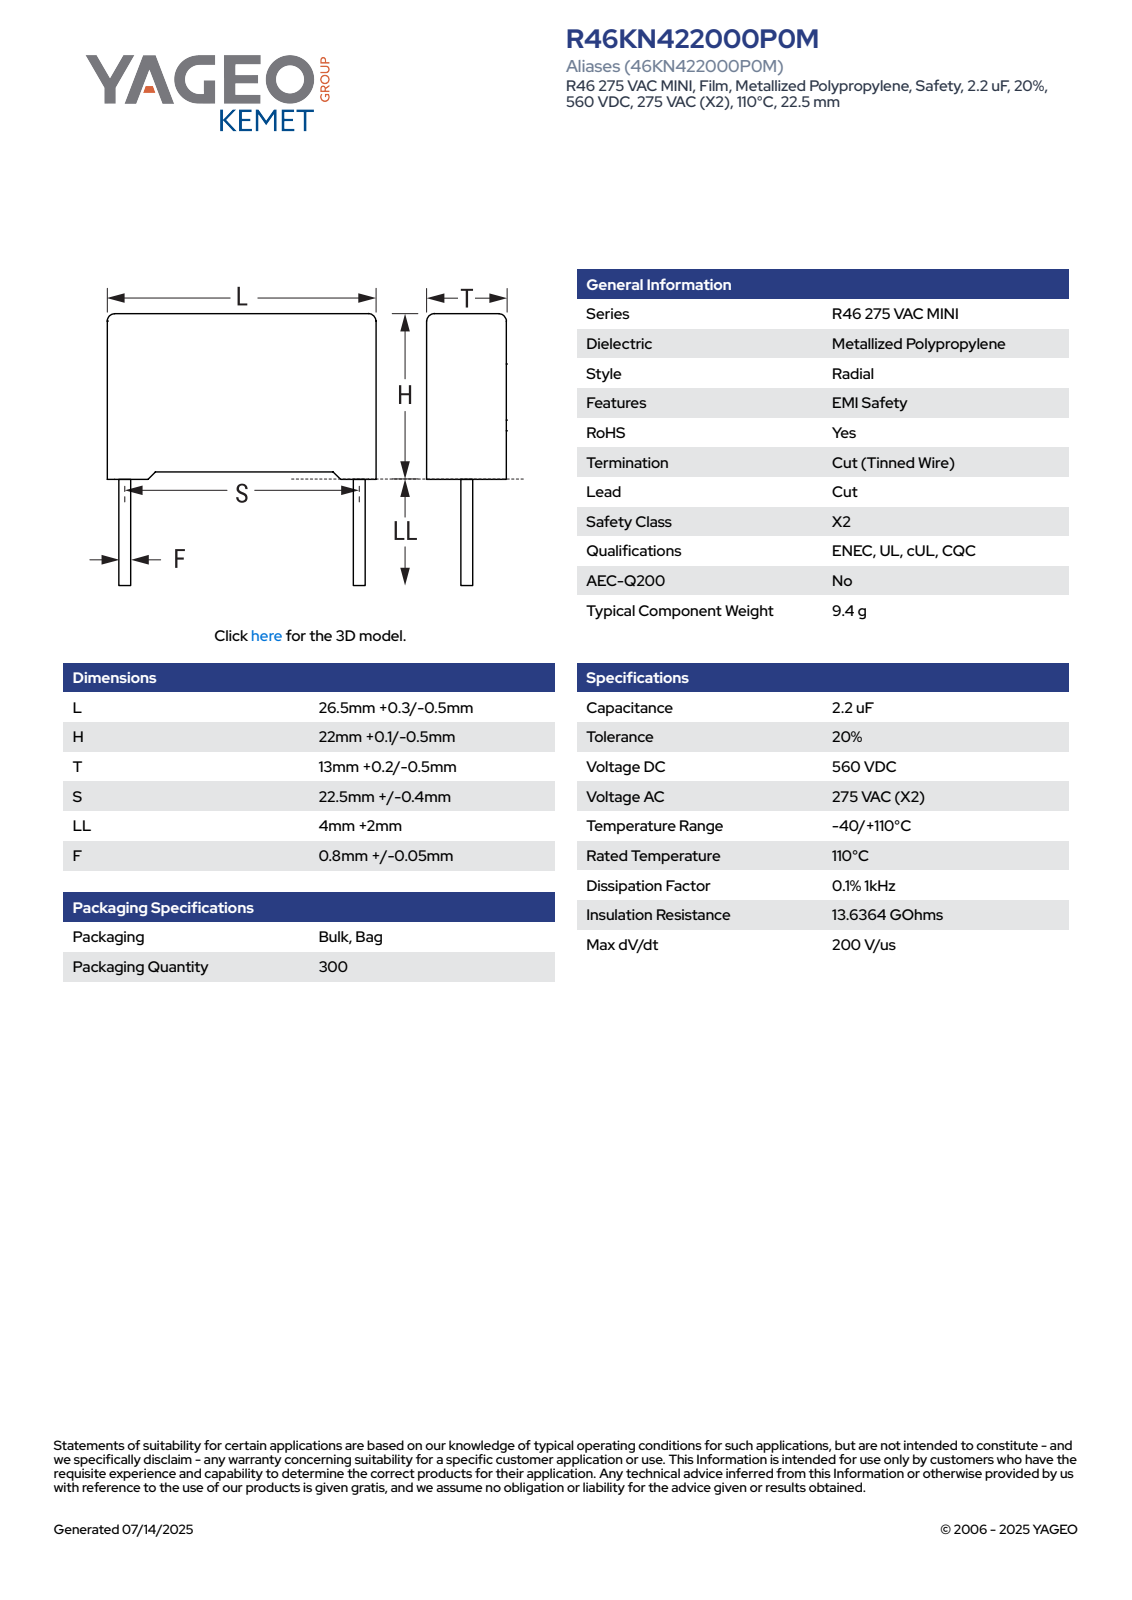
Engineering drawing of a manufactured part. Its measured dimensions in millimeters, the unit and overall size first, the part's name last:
Units: millimetres
Overall size (bounding box): 28.1 × 26.8 × 13.21
Round bosses / shafts (diameter × count): ⌀0.85 ×2
Partial cylindrical surfaces — rounded edges, fillets, slot ends (radius × count): R0.5 ×4
Main face-to-face distances: 13.2, 26.8, 21.34, 21.35, 0.75, 0.76, 22.1, 0.89, 25.91, 13.21
Volume: 7 580 mm³ · Surface area: 2 547 mm²
Bodies: 4 solids, 85 faces (77 planar, 8 cylindrical, 0 other)
Part name (STEP PRODUCT): CFR_RB2_26.5X22X13_L26.8H22.1T13.2S22.5LL6F0.85
STEP written by: SolidWorks 2021 (AUTOMOTIVE_DESIGN)
